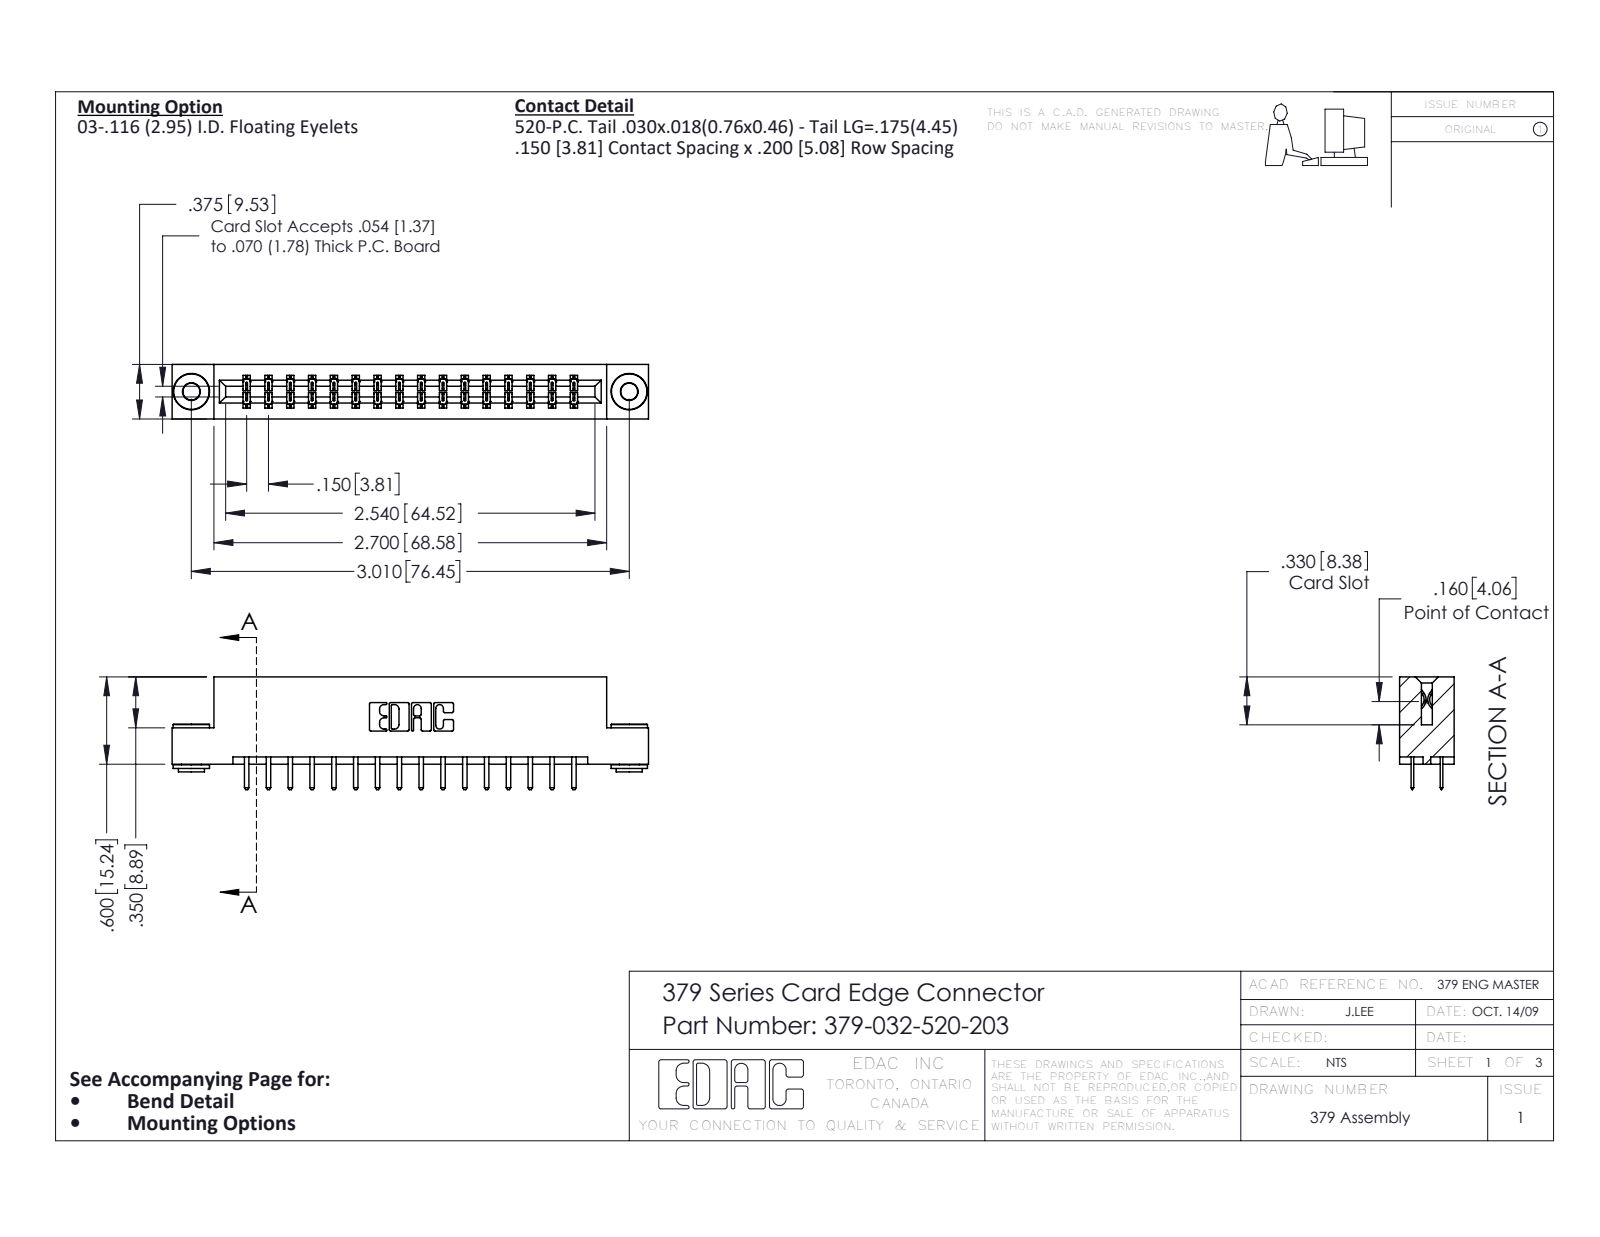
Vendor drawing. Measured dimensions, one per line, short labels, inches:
name: 345-250-002_345-250-002-102; 345-292-001_345-293-120; 379-032-520-203; 379 Part_Flush - .156 Dia - TH
written by: SolidWorks 2020 (CONFIG_CONTROL_DESIGN)
unit: in
bodies: 35 solids, 1944 faces (1296 planar, 640 cylindrical, 8 other)
size: 3.275 × 0.775 × 0.375
volume: 0.521 in³; area: 14.78 in²
holes: 2× ⌀0.116, 2× ⌀0.156
bosses: 2× ⌀0.25, 2× ⌀0.18, 2× ⌀0.136
rounds: 63× R0.006, 36× R0.01, 22× R0.01, 6× R0.007, 6× R0.031, 3× R0.026, 2× R0.014, 2× R0.022
face distances: 0.3, 0.2, 0.375, 0.075, 0.1, 0.15, 0.05, 0.6, 0.225, 0.55
hole spacings: 3.01
